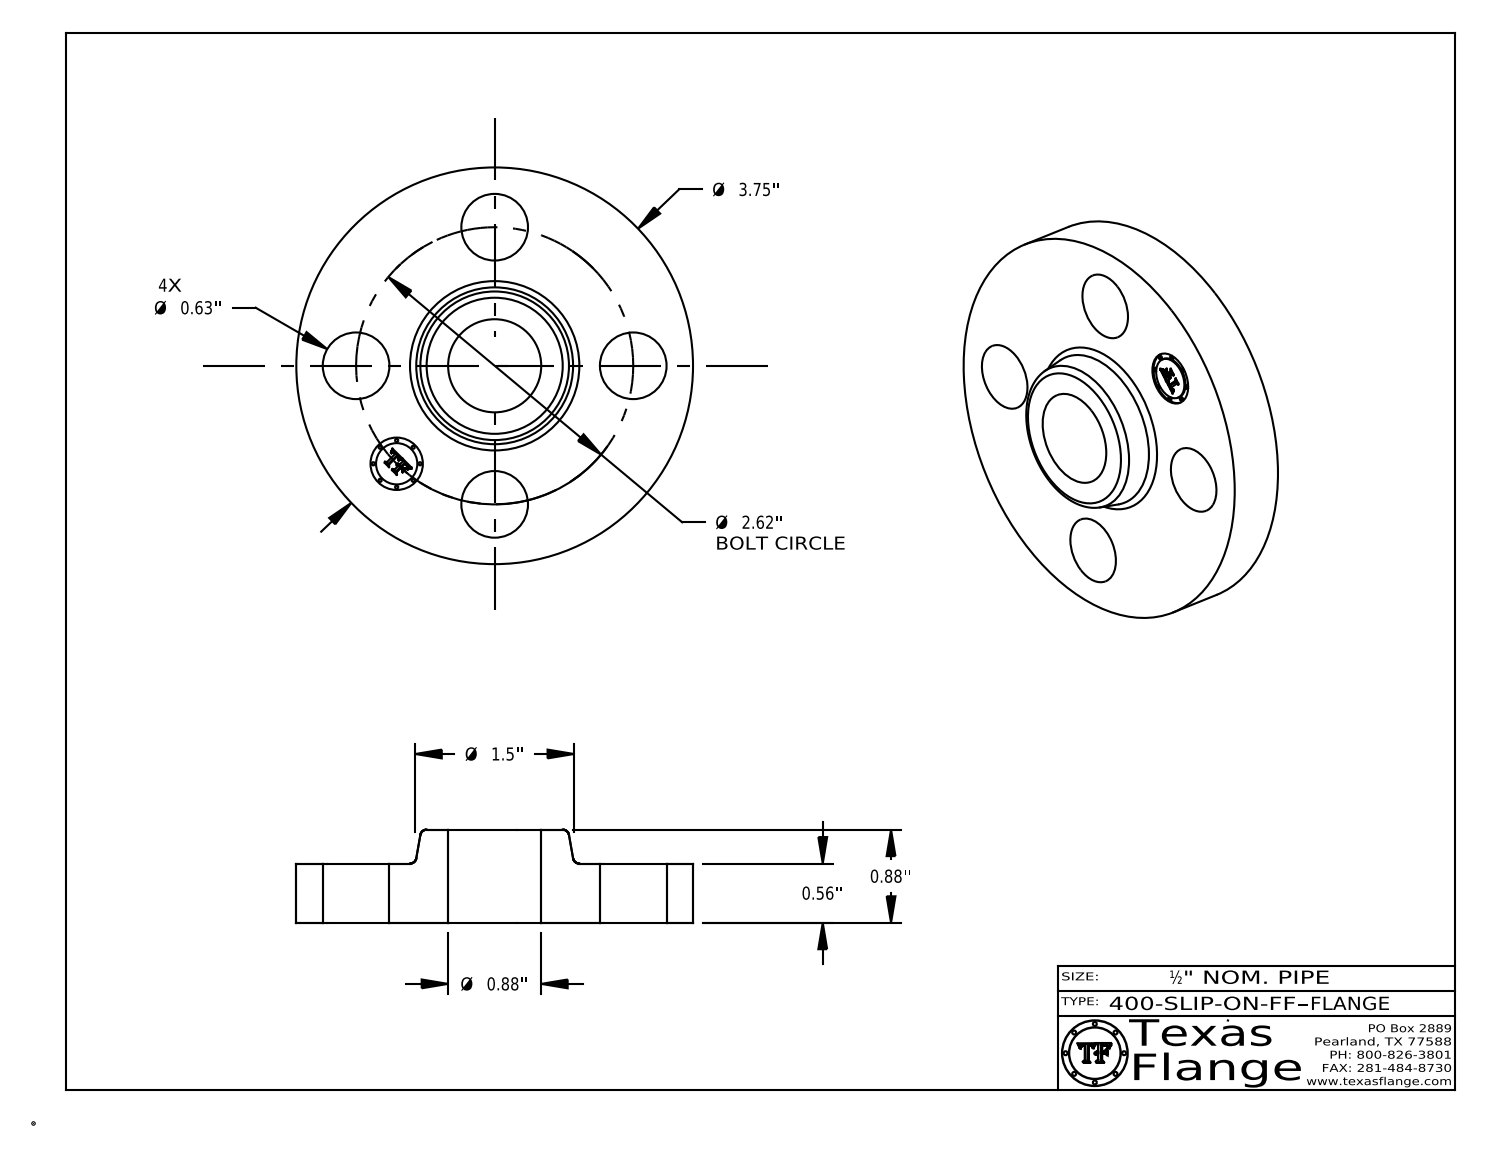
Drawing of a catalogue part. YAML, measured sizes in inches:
part_name: "400-SLIP-ON-FF"
step_written_by: "CATIA V5 STEP AP214 (AUTOMOTIVE_DESIGN)"
units: inches
bodies: {solids: 1, faces: 406, planar: 368, cylindrical: 32, other: 6}
overall_size: [3.75, 3.75, 0.88]
volume: 5.475
surface_area: 33
round_holes:
  - {diameter: 0.63, count: 4}
  - {diameter: 0.495, count: 1}
  - {diameter: 0.88, count: 1}
round_bosses_or_shafts:
  - {diameter: 0.03, count: 8}
  - {diameter: 3.75, count: 1}
  - {diameter: 0.39, count: 1}
face_to_face_distances: [0.56, 0.88, 0.32, 0.545, 0.015, 0.335, 0.148, 0.144, 0.027, 0.096]
hole_center_spacings: [1.31, 1.852, 1.003, 2.42, 2.62, 1.31]
